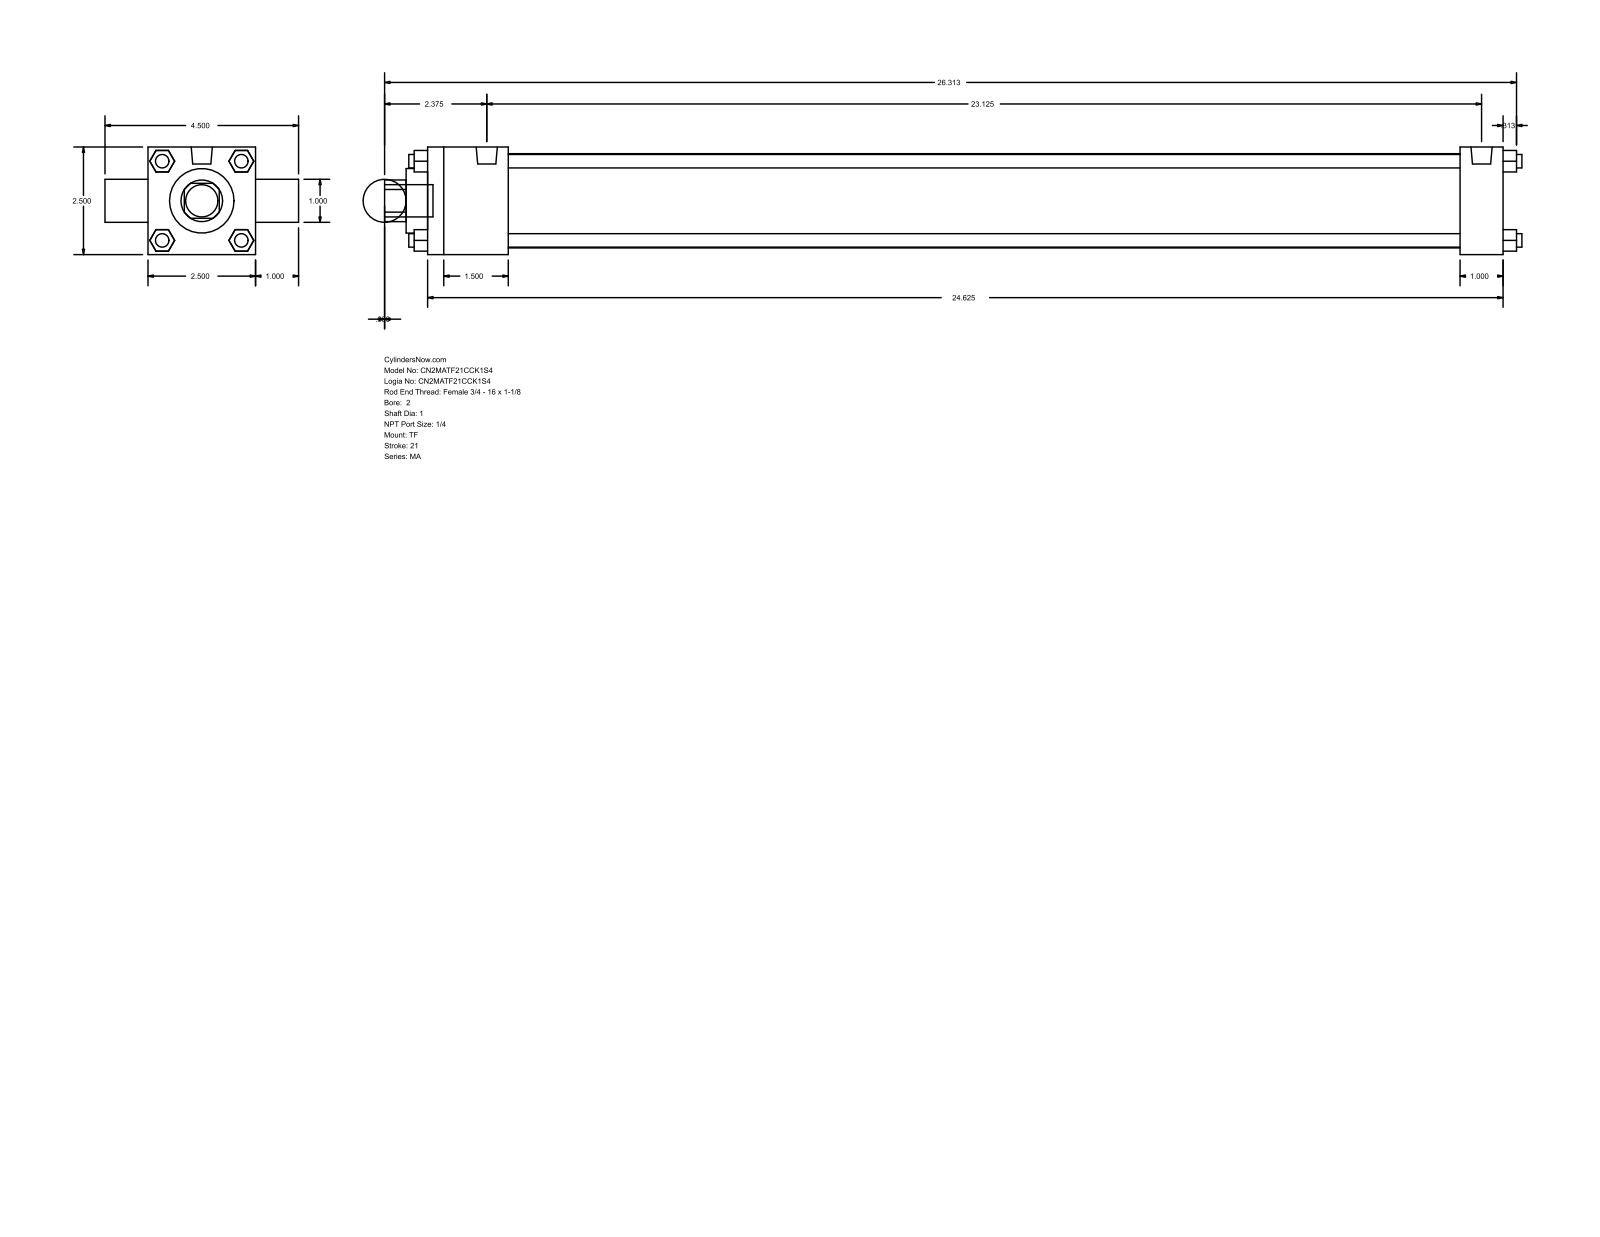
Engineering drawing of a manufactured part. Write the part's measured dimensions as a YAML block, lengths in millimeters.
part_name: "MA_TF__0200_1"
step_written_by: "GSSL Pune (CONFIG_CONTROL_DESIGN)"
units: millimeters
bodies: {solids: 0, faces: 120, planar: 92, cylindrical: 28, other: 0}
overall_size: [671.51, 114.3, 63.5]
round_holes:
  - {diameter: 25.4, count: 2}
  - {diameter: 38.1, count: 1}
  - {diameter: 55.63, count: 1}
round_bosses_or_shafts:
  - {diameter: 7.94, count: 7}
  - {diameter: 12.49, count: 2}
  - {diameter: 19.05, count: 1}
partial_cylinders:
  - {radius: 12.29, count: 1}
face_to_face_distances: [63.5, 25.4, 635, 12.7, 47.63, 609.6, 561.97, 587.37, 88.9, 40.47]
